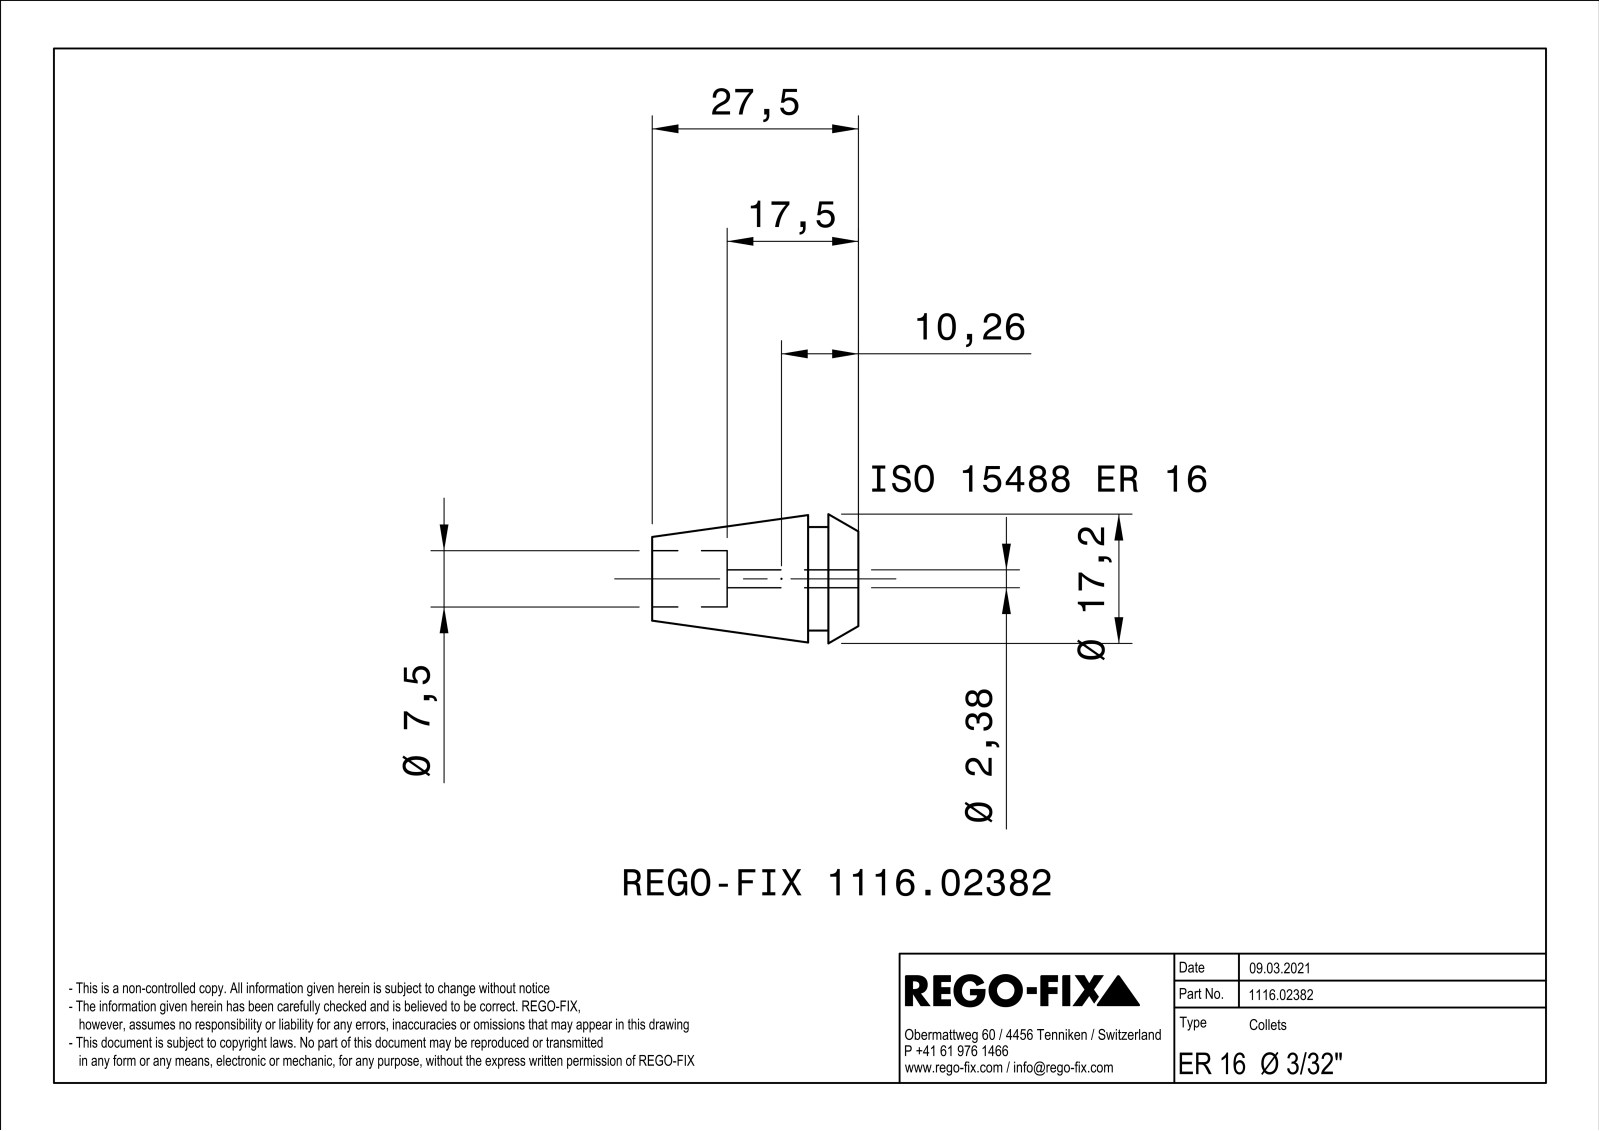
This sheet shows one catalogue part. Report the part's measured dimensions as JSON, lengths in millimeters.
{"part_name": "NOCUT", "step_written_by": "SIEMENS PLM Software Solid Edge ST10 (AUTOMOTIVE_DESIGN)", "units": "millimeters", "bodies": {"solids": 1, "faces": 240, "planar": 112, "cylindrical": 32, "other": 96}, "overall_size": [27.5, 17.24, 17.24], "volume_mm3": 3081, "surface_area_mm2": 5211, "round_holes": [[7.5, 1]], "round_bosses_or_shafts": [[13.8, 1]], "partial_cylinders_radius": [[1.19, 1]], "face_to_face_distances": [0.44, 0.46, 0.45, 4, 6.7, 2.7, 3.27, 3.28, 3.72, 3.73]}
